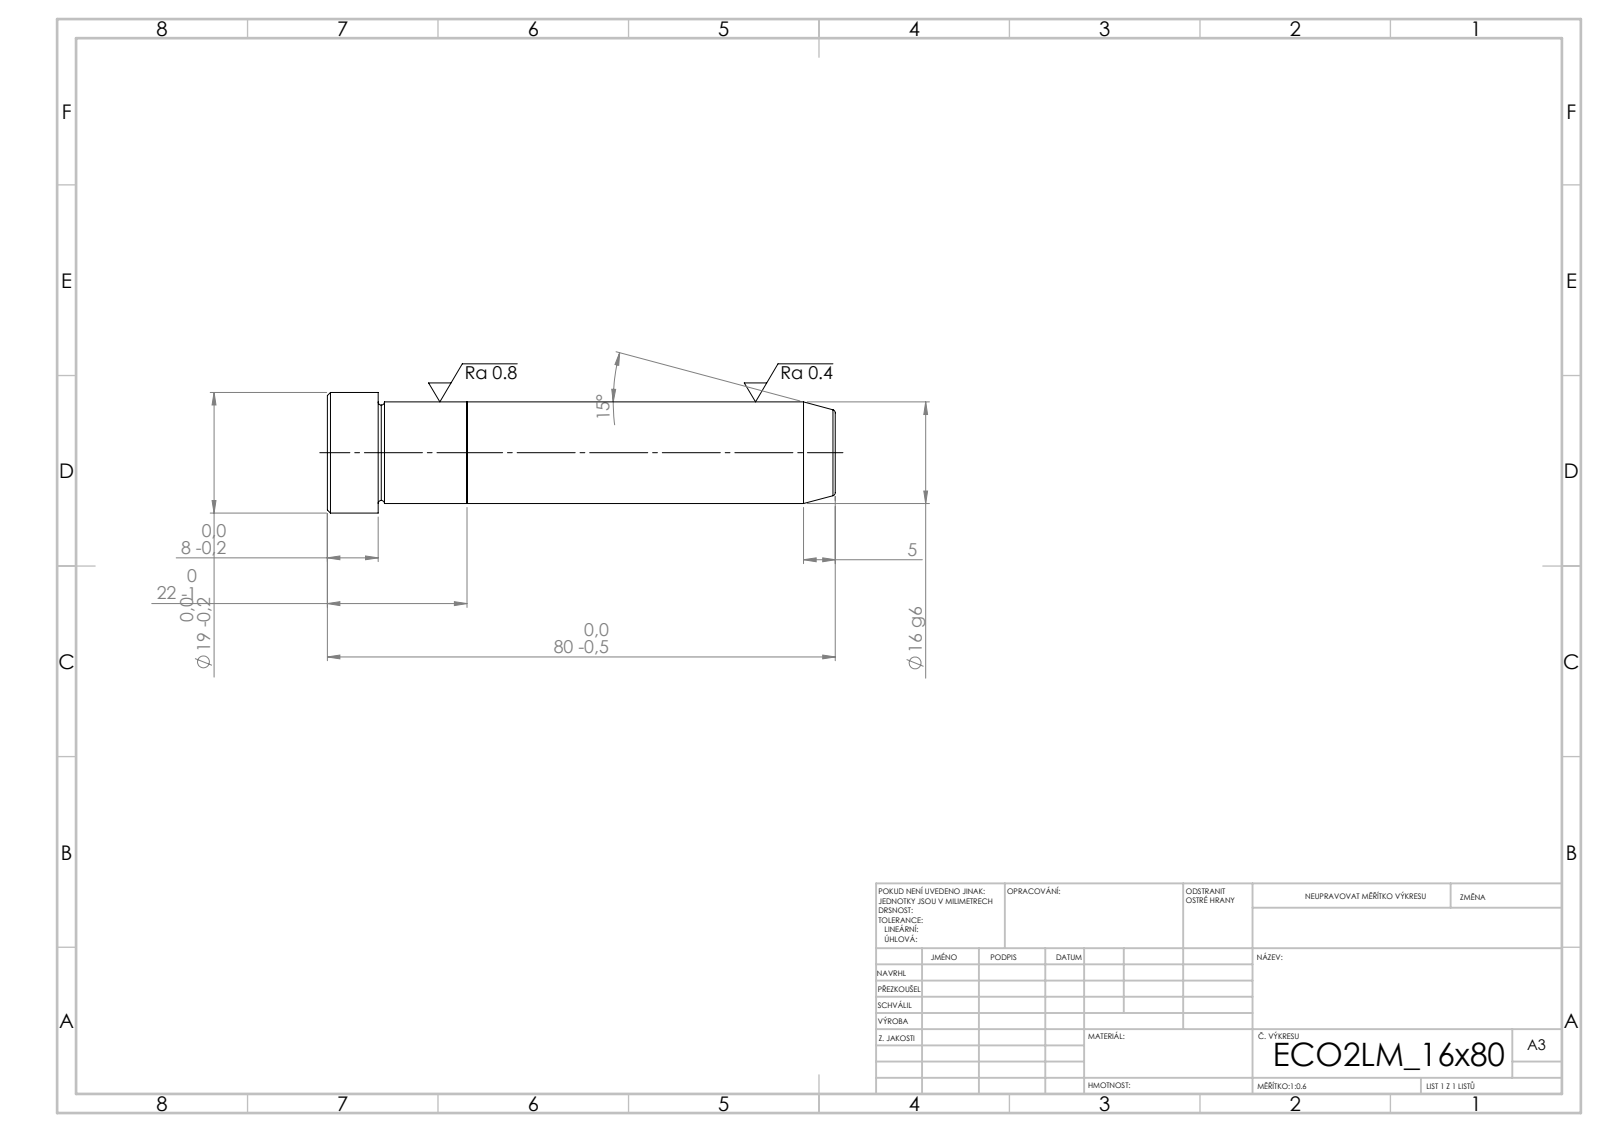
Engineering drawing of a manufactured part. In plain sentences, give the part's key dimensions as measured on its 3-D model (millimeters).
Its 3-D file was written by "SolidWorks 2019 (CONFIG_CONTROL_DESIGN)". It is 2 solids with 21 faces: 5 planar, 6 cylindrical and 10 other. Overall it measures 80 by 19 by 19 millimeters. Its volume is 16 558 cubic millimeters and its surface area 4 994 square millimeters. Round bosses or shafts: 1 of diameter 19, 1 of diameter 16. The main face-to-face distances are 22, 58, 80, 72, 14, 8.
